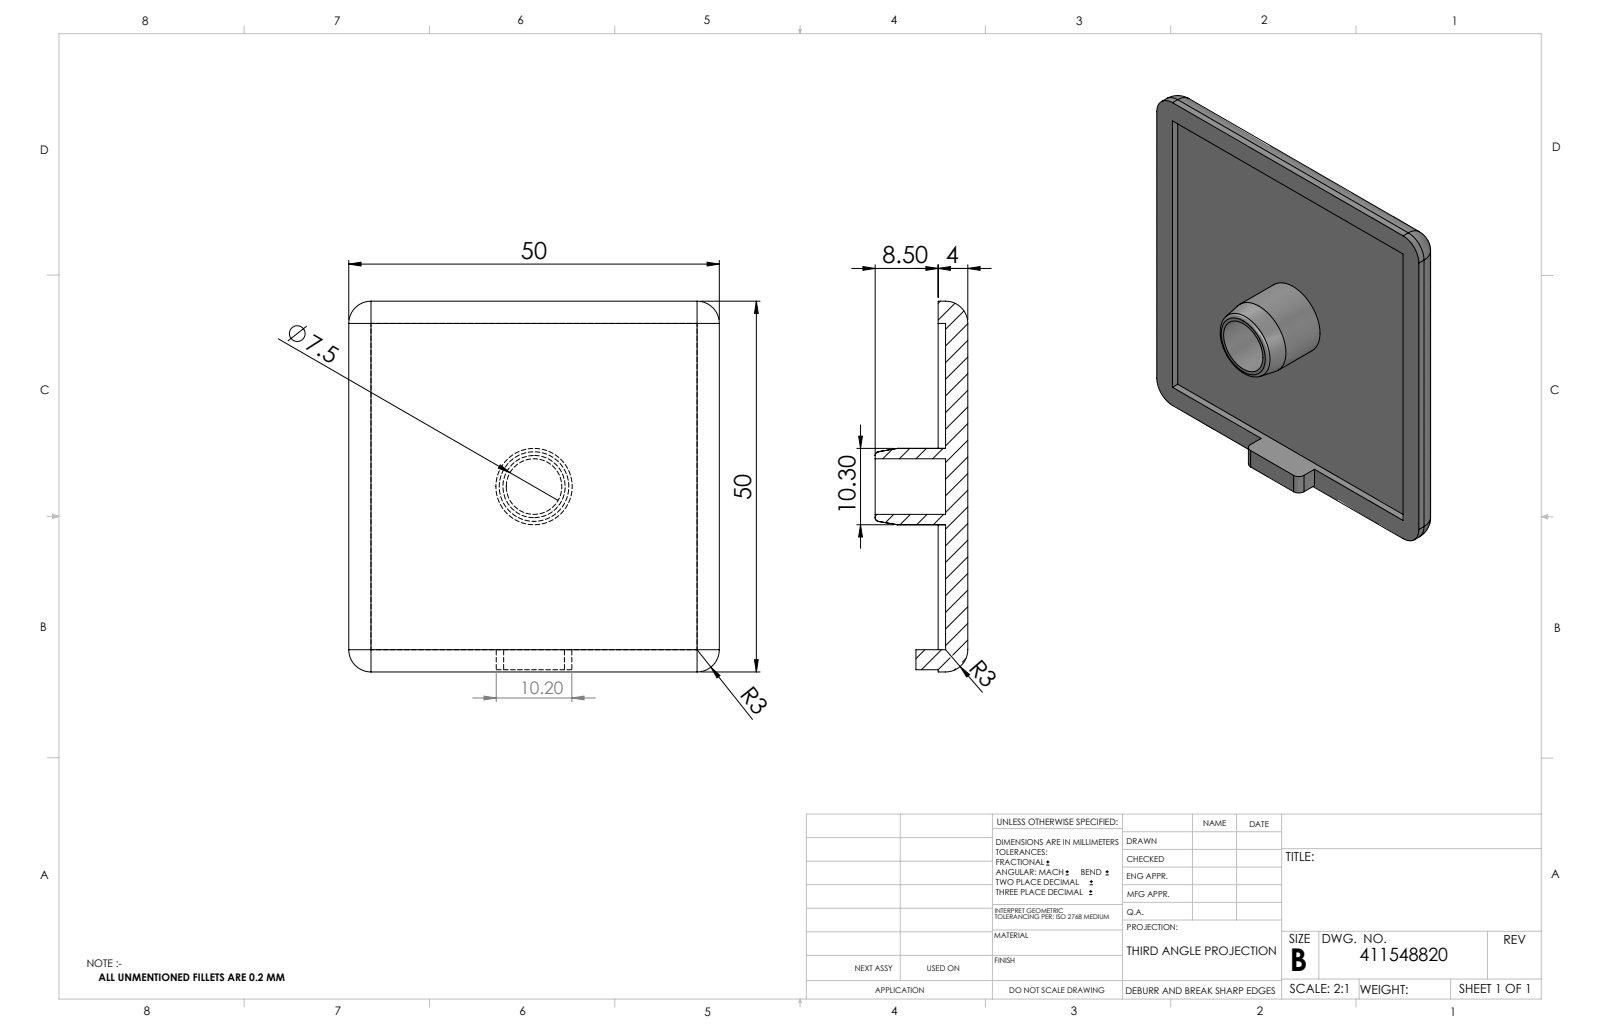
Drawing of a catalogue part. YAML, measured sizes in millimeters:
part_name: "411548820"
step_written_by: "SolidWorks 2014 (CONFIG_CONTROL_DESIGN)"
units: millimeters
bodies: {solids: 1, faces: 39, planar: 17, cylindrical: 14, other: 8}
overall_size: [50, 50, 12.5]
volume: 8092
surface_area: 6267
round_holes:
  - {diameter: 7.5, count: 1}
round_bosses_or_shafts:
  - {diameter: 10.3, count: 1}
partial_cylinders:
  - {radius: 3, count: 8}
  - {radius: 1, count: 2}
face_to_face_distances: [3, 4, 1, 47, 50, 44, 2.7, 46.7, 49.7, 7]
